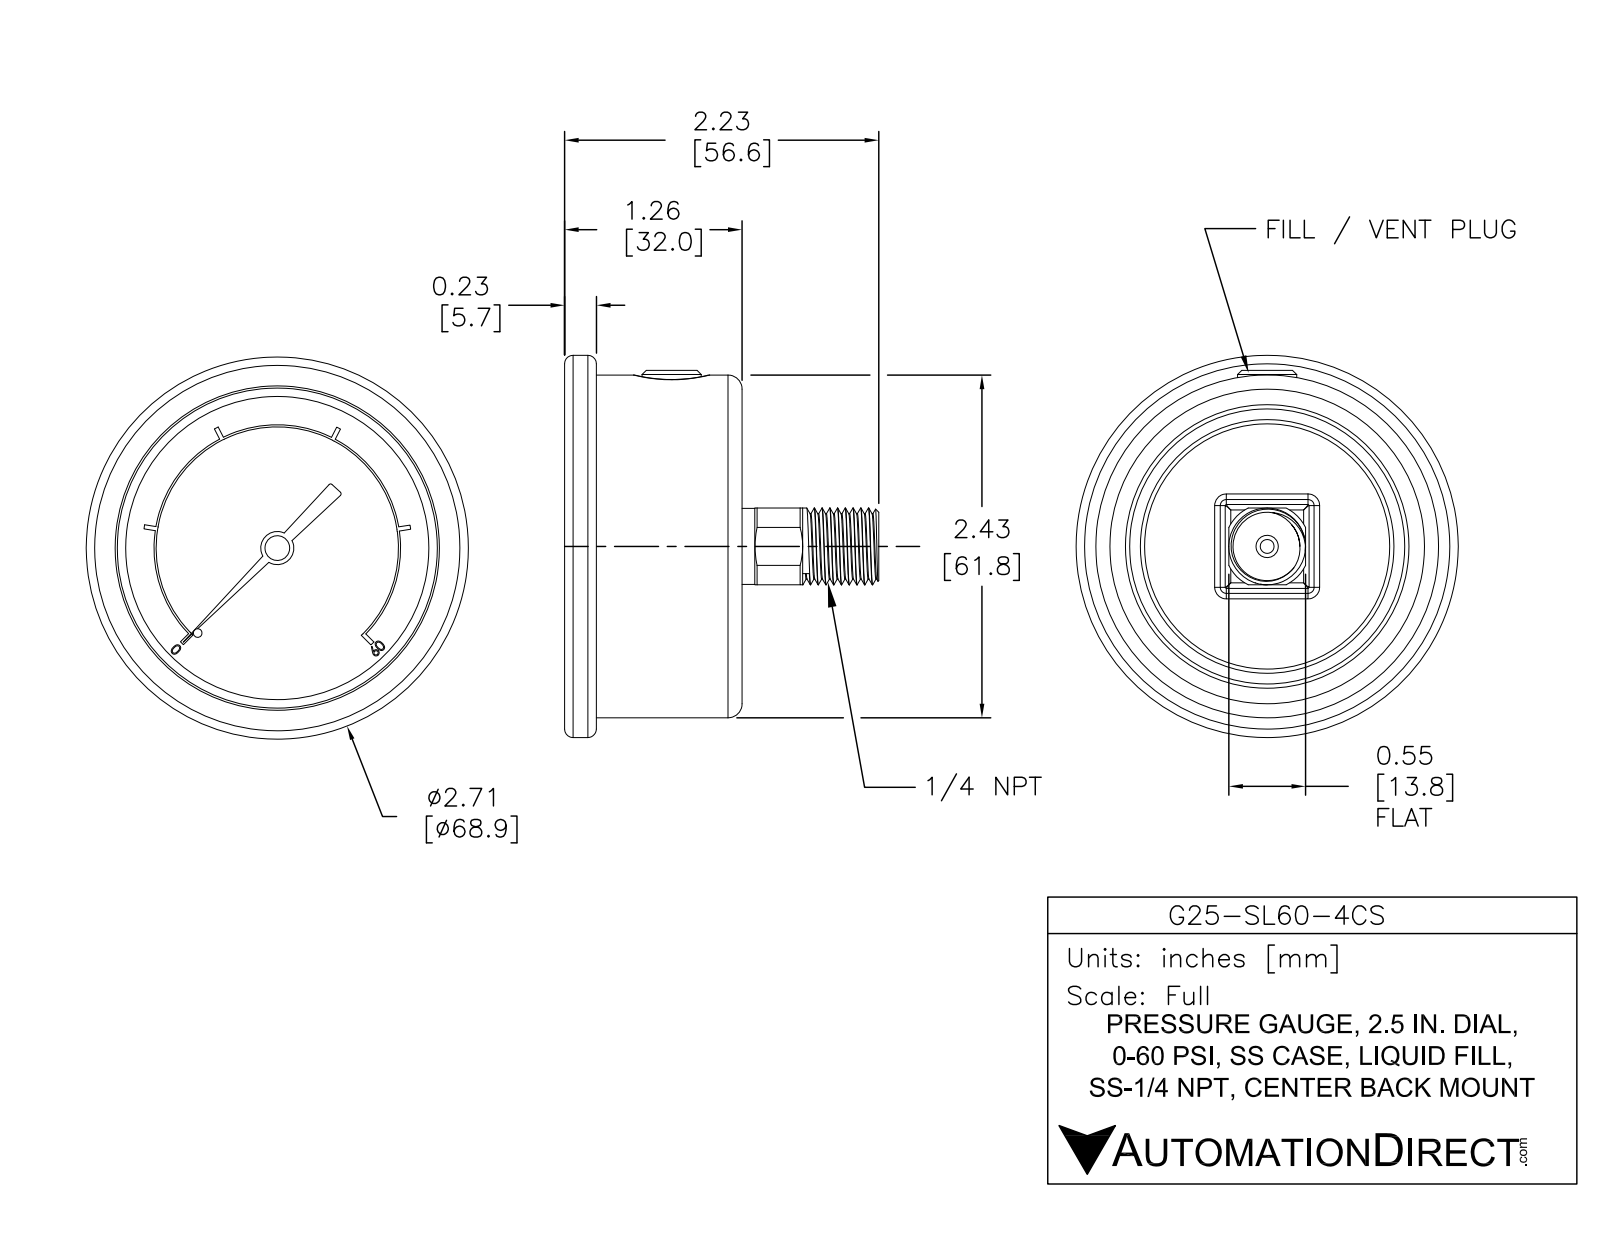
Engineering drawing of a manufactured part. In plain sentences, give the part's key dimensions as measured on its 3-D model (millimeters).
The part is named "G25-SL60-4CS". Its 3-D file was written by "SolidWorks 2021 (AUTOMOTIVE_DESIGN)". It is 1 solid with 344 faces: 204 planar, 83 cylindrical and 57 other. Overall it measures 68.9 by 68.9 by 56.6 millimeters. Its volume is 84 690 cubic millimeters and its surface area 16 010 square millimeters. Round holes: 1 of diameter 1.8, 1 of diameter 2.5, 1 of diameter 57.7. Round bosses or shafts: 1 of diameter 68.9, 1 of diameter 61.8, 1 of diameter 13.8, 1 of diameter 13.7, 1 of diameter 10.7, 1 of diameter 6, 1 of diameter 4.5, 1 of diameter 3.6. Partial cylindrical surfaces (rounded edges, fillets, slot ends): 8 of radius 1.5, 2 of radius 0.4, 1 of radius 7.7, 1 of radius 21.8, 1 of radius 22.2. The main face-to-face distances are 24.1, 30.5, 6.4, 1.5, 25.7, 32, 26.3, 24.8, 0.6, 5.7.
